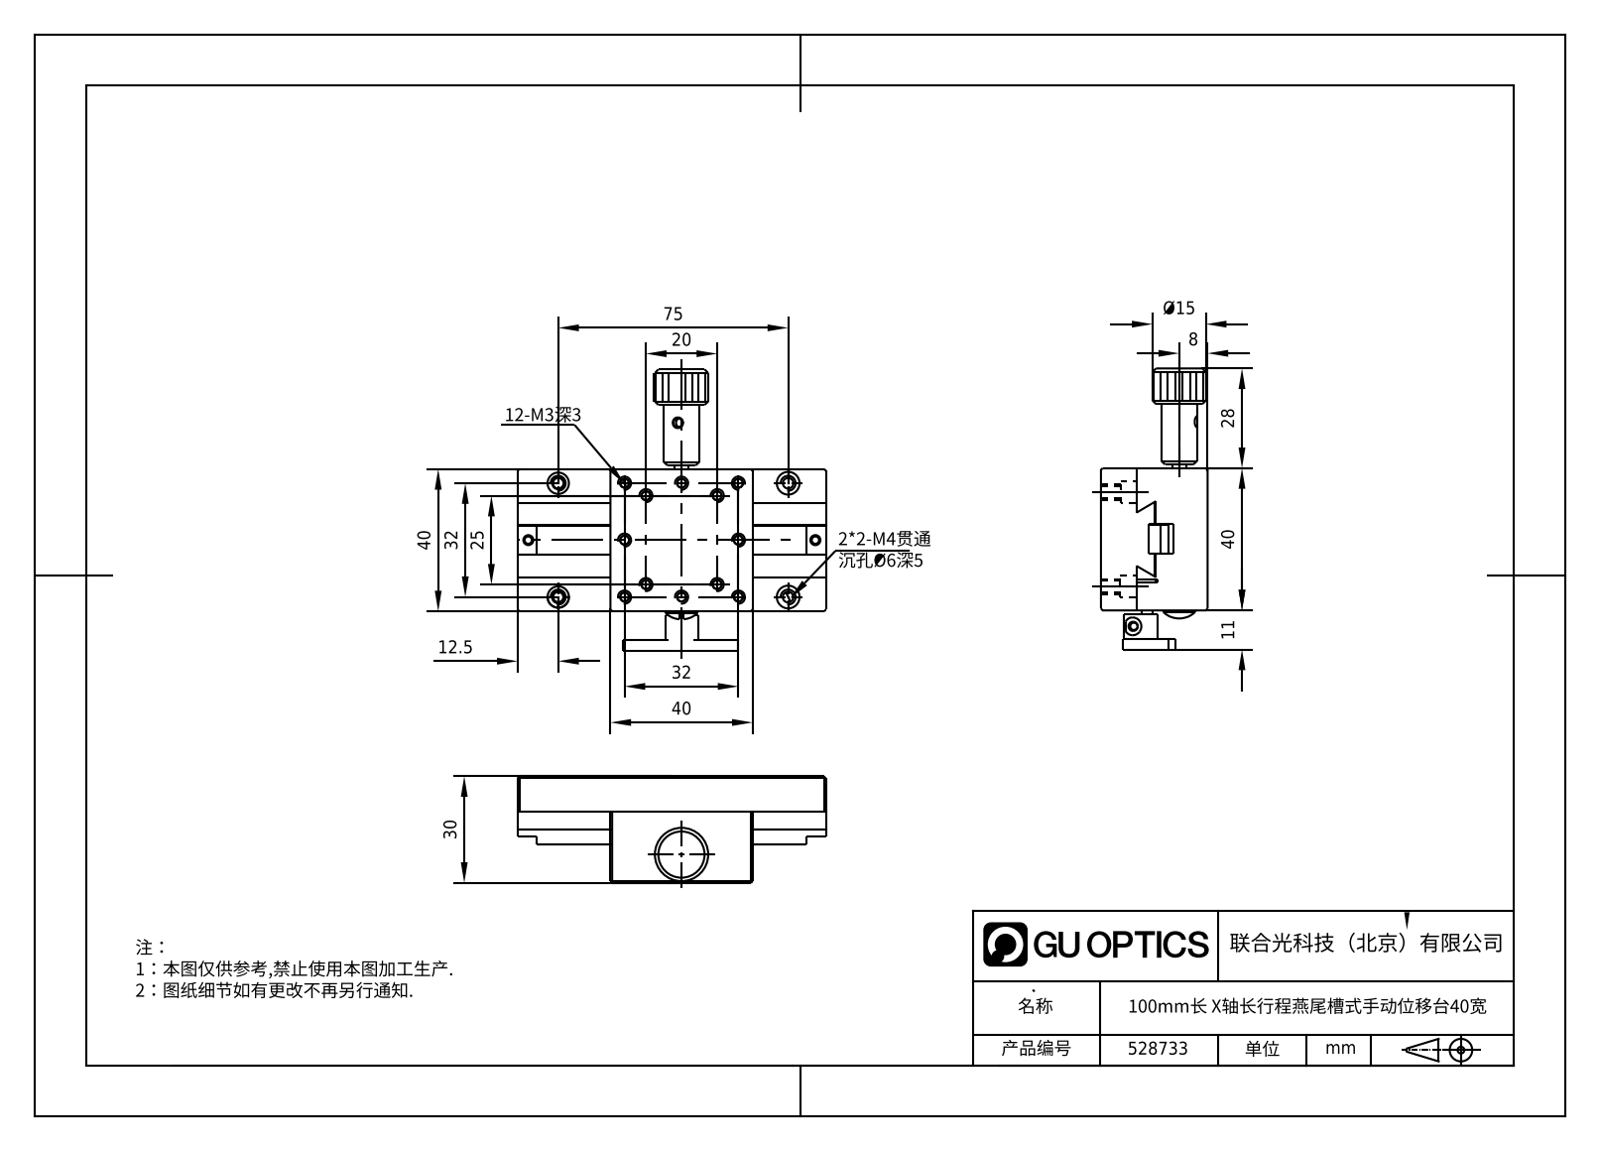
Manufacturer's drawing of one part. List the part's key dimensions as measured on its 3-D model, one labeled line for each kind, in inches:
Part name (STEP PRODUCT): 528733
STEP written by: SolidWorks 2020 (CONFIG_CONTROL_DESIGN)
Units: inches
Bodies: 19 solids, 1916 faces (1177 planar, 223 cylindrical, 516 other)
Overall size (bounding box): 3.937 × 3.366 × 1.223
Volume: 6.616 in³ · Surface area: 65.04 in²
Round holes (diameter × count): ⌀0.098 ×18, ⌀0.13 ×5, ⌀0.081 ×4, ⌀0.236 ×4, ⌀0.114 ×3, ⌀0.157 ×1, ⌀0.161 ×1, ⌀0.177 ×1, ⌀0.197 ×1, ⌀0.315 ×1
Round bosses / shafts (diameter × count): ⌀0.098 ×3, ⌀0.354 ×2, ⌀0.177 ×2, ⌀0.118 ×2, ⌀0.394 ×1, ⌀0.315 ×1, ⌀0.291 ×1, ⌀0.27 ×1
Partial cylindrical surfaces — rounded edges, fillets, slot ends (radius × count): R0.041 ×8, R0.039 ×3, R0.098 ×2, R0.008 ×1, R0.047 ×1, R0.394 ×1
Main face-to-face distances: 1.575, 0.413, 1.181, 0.768, 0.508, 0.094, 0.673, 0.197, 0.583, 0.598
Hole centre spacings: 0.63, 1.26, 1.409, 0.274, 0.417, 0.546, 0.704, 0.733
